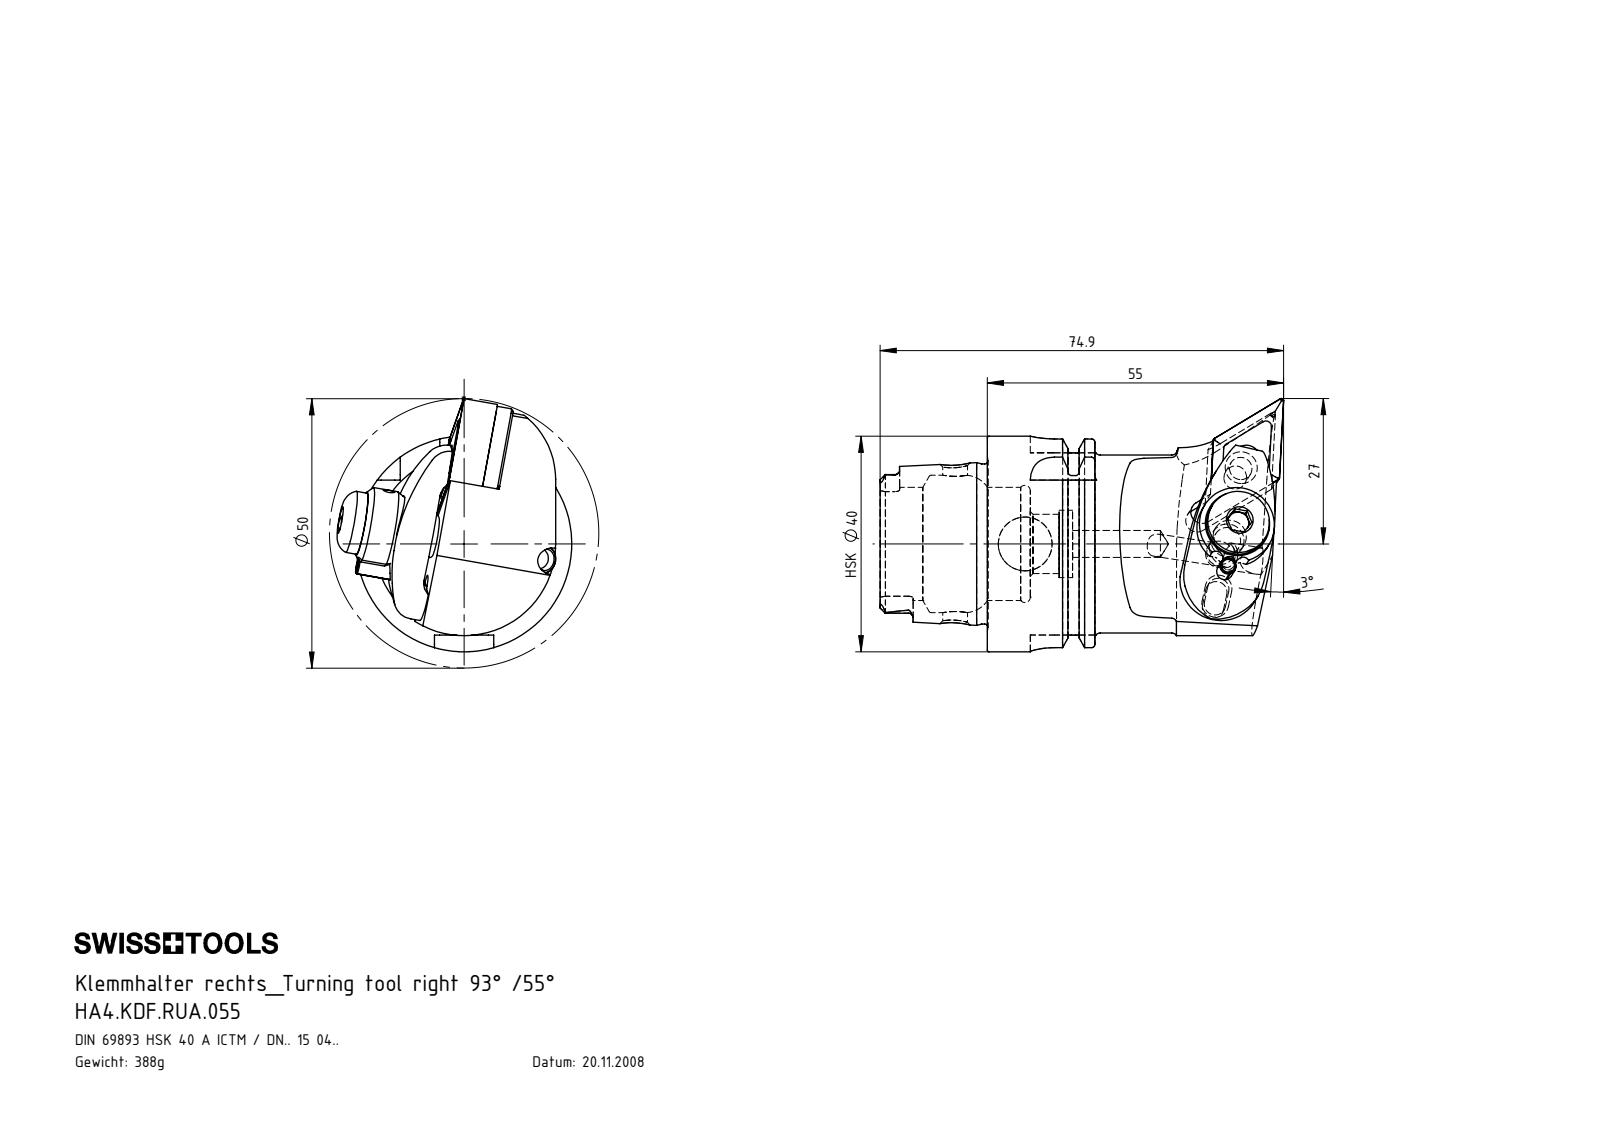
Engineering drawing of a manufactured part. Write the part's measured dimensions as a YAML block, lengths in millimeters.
part_name: "WCC-ER5.102.005_A; HA4-KDF.RUA.055_C_Fertigbearbeitung; WCC-ER5.102.012_B; WCC-ER2.001.010_A (+7 more)"
step_written_by: "SolidWorks 2017 (AUTOMOTIVE_DESIGN)"
units: millimeters
bodies: {solids: 11, faces: 468, planar: 125, cylindrical: 154, other: 189}
overall_size: [74.9, 47, 43.57]
volume: 50395
surface_area: 19413
round_holes:
  - {diameter: 2, count: 3}
  - {diameter: 5, count: 3}
  - {diameter: 4.2, count: 2}
  - {diameter: 7, count: 2}
  - {diameter: 2.4, count: 1}
  - {diameter: 3, count: 1}
  - {diameter: 4, count: 1}
  - {diameter: 4.6, count: 1}
  - {diameter: 5.16, count: 1}
  - {diameter: 6.2, count: 1}
  - {diameter: 6.5, count: 1}
  - {diameter: 8.5, count: 1}
round_bosses_or_shafts:
  - {diameter: 5, count: 2}
  - {diameter: 3, count: 2}
  - {diameter: 40, count: 1}
  - {diameter: 34.75, count: 1}
  - {diameter: 33, count: 1}
  - {diameter: 29.71, count: 1}
  - {diameter: 14, count: 1}
  - {diameter: 11.5, count: 1}
partial_cylinders:
  - {radius: 0.39, count: 6}
  - {radius: 0.69, count: 6}
  - {radius: 0.9, count: 6}
  - {radius: 0.4, count: 5}
  - {radius: 4.5, count: 4}
  - {radius: 1.5, count: 3}
  - {radius: 3, count: 3}
  - {radius: 1.82, count: 2}
face_to_face_distances: [6.02, 0.49, 7.95, 1.31, 7.33, 12, 9.2, 12.21, 12.7, 19.95]
hole_center_spacings: [23, 7.99, 8.01, 8.19, 14.81, 15, 15.01, 23.01]
